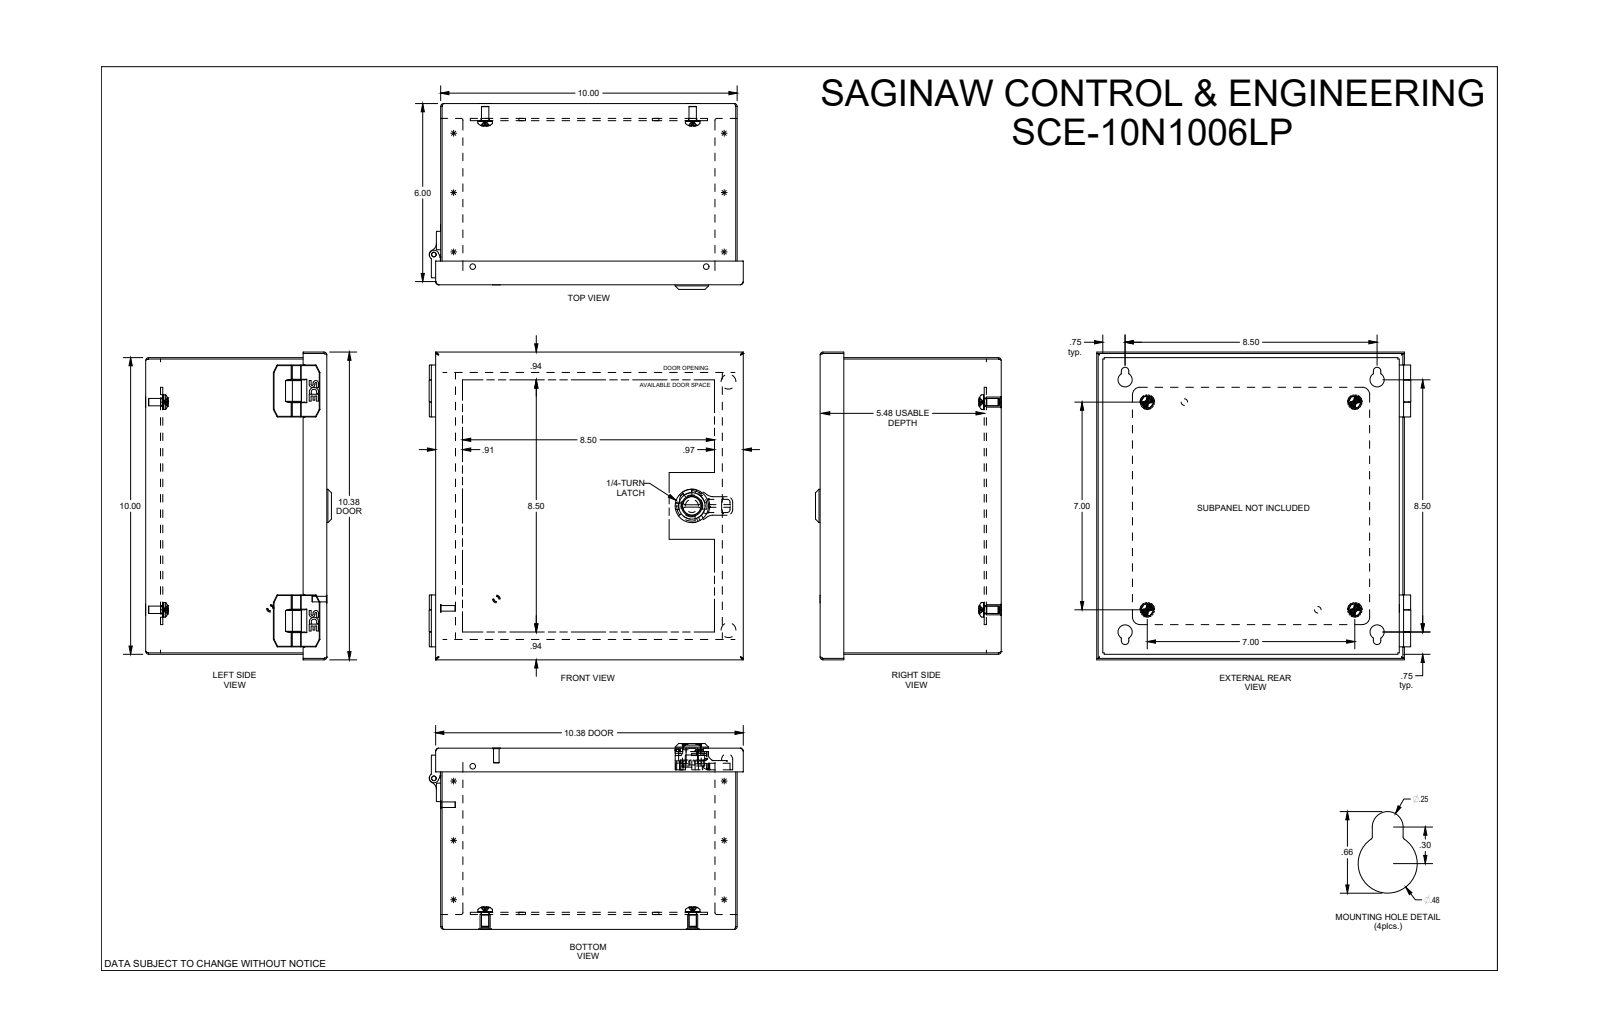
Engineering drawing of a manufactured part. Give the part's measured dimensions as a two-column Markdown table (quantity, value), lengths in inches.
| quantity | value |
| --- | --- |
| part name | SCE-10N1006LP |
| STEP written by | SolidWorks 2019 (AUTOMOTIVE_DESIGN) |
| units | inches |
| bodies | 31 solids, 1547 faces (578 planar, 645 cylindrical, 324 other) |
| overall size | 10.592 × 10.375 × 6.267 |
| volume | 36.06 in³ |
| surface area | 1 157 in² |
| round holes (diameter × count) | 0.17 × 4, 0.25 × 4, 0.281 × 4, 0.329 × 4, 0.343 × 4, 0.48 × 4, 0.193 × 3, 0.187 × 2, 0.218 × 2, 0.158 × 1, 0.44 × 1, 0.635 × 1 |
| round bosses / shafts (diameter × count) | 0.492 × 4, 0.479 × 4, 0.341 × 4, 0.248 × 4, 0.237 × 4, 0.16 × 4, 0.5 × 2, 0.323 × 2 |
| partial cylindrical surfaces (radius × count) | 0.01 × 253, 0.02 × 95, 0.06 × 25, 0.015 × 24, 0.025 × 24, 0.055 × 6, 0.25 × 6, 0.125 × 4 |
| main face-to-face distances | 0.06, 9.94, 6.048, 10, 9.88, 5.989, 6.108, 0.5, 0.44, 0.575 |
| hole center spacings | 7.786, 1.061, 1.51, 7, 7.75, 8.5, 10.96, 7.75 |
